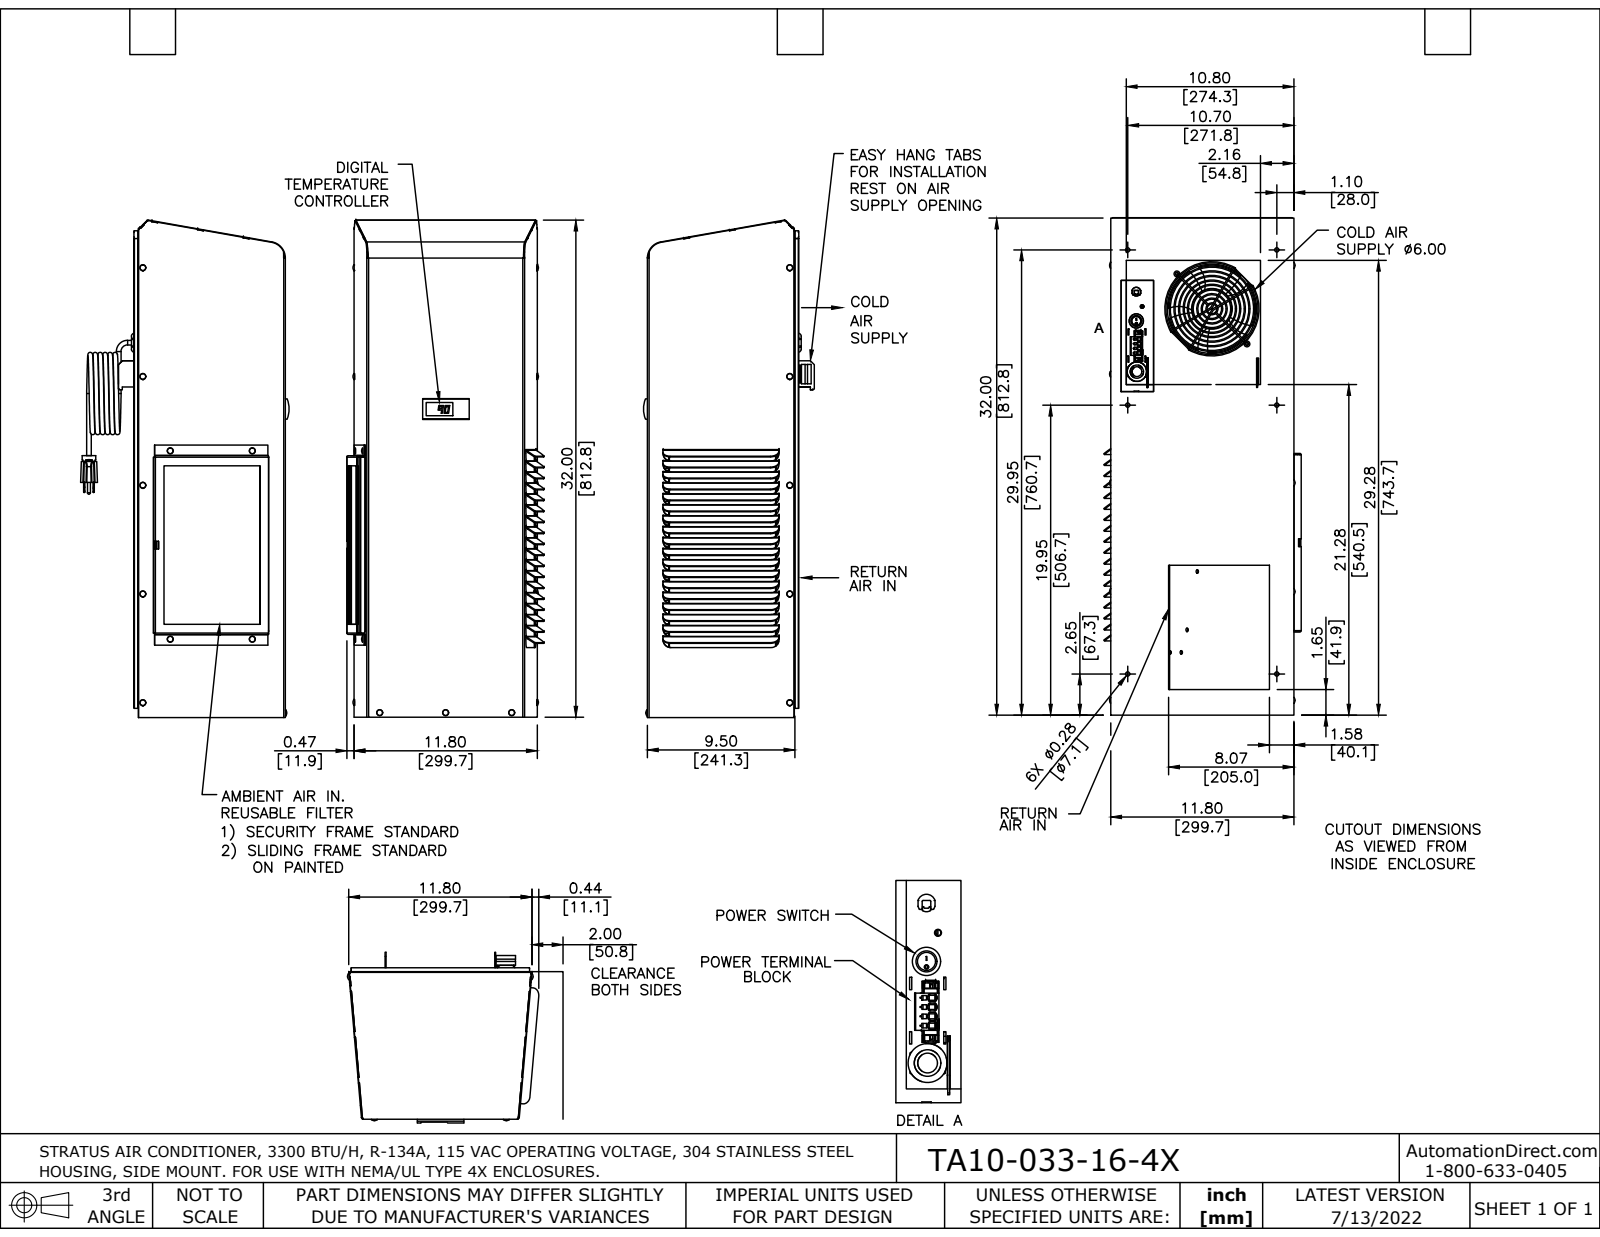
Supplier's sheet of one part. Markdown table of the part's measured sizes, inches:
| quantity | value |
| --- | --- |
| part name | TA10-033-16-4X |
| STEP written by | SolidWorks 2021 (AUTOMOTIVE_DESIGN) |
| units | inches |
| bodies | 1 solid, 1742 faces (1077 planar, 495 cylindrical, 170 other) |
| overall size | 32.024 × 12.576 × 11.554 |
| volume | 136.5 in³ |
| surface area | 3 197 in² |
| round holes (diameter × count) | 0.159 × 11, 0.204 × 5, 6 × 1 |
| round bosses / shafts (diameter × count) | 0.19 × 7, 0.353 × 2, 0.248 × 2, 6.07 × 1, 0.906 × 1, 0.384 × 1, 0.377 × 1, 0.087 × 1 |
| partial cylindrical surfaces (radius × count) | 0.015 × 45, 0.01 × 42, 0.5 × 36, 0.506 × 36, 0.1 × 28, 0.058 × 21, 0.116 × 21, 0.03 × 13 |
| main face-to-face distances | 0.058, 9.377, 9.435, 0.054, 9.431, 9.489, 0.058, 0.373, 0.254, 0.308 |
| hole center spacings | 7, 14, 21, 5.3, 6.565, 12.12, 1.731, 1.733 |
